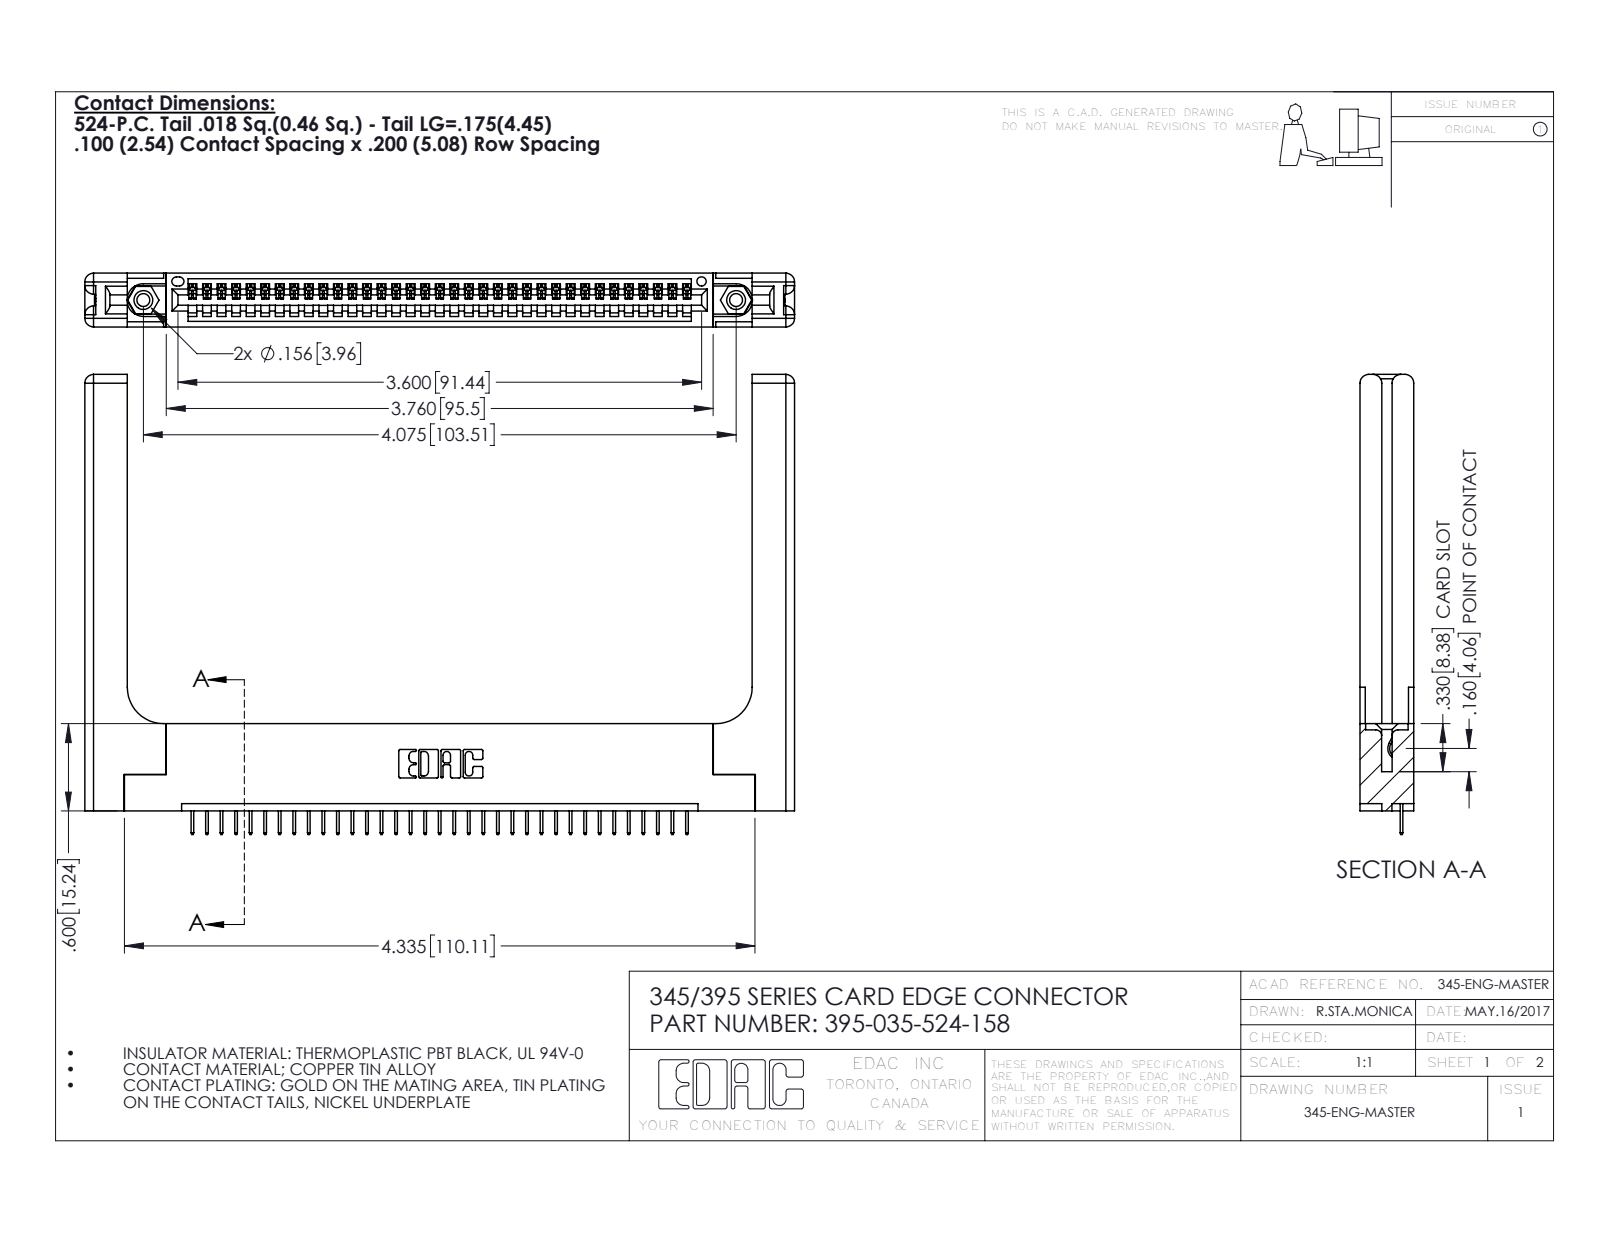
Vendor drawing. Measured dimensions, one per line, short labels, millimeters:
name: 345 Part_Flush Mounting Lugs - 0.156 Dia-TH; 345-250-001_345-250-001-102; 345-292-001_345-293-124; 395-035-524-158 (+1 more)
written by: SolidWorks 2016 (CONFIG_CONTROL_DESIGN)
unit: mm
bodies: 40 solids, 2552 faces (1838 planar, 654 cylindrical, 60 other)
size: 123.9 × 80.3 × 9.4
volume: 20 070 mm³; area: 20 150 mm²
holes: 2× ⌀2.3, 2× ⌀3.2, 2× ⌀4, 1× ⌀1.6
bosses: 2× ⌀3.9
rounds: 70× R0.2, 22× R0.3, 16× R1.5, 6× R0.2, 6× R0.8, 3× R0.7, 2× R0.8, 2× R0.8
face distances: 9.4, 1.8, 7.6, 5.1, 2.5, 6.9, 0.6, 3.8, 3.8, 5.7
hole spacings: 6.9, 97.5, 103.5
